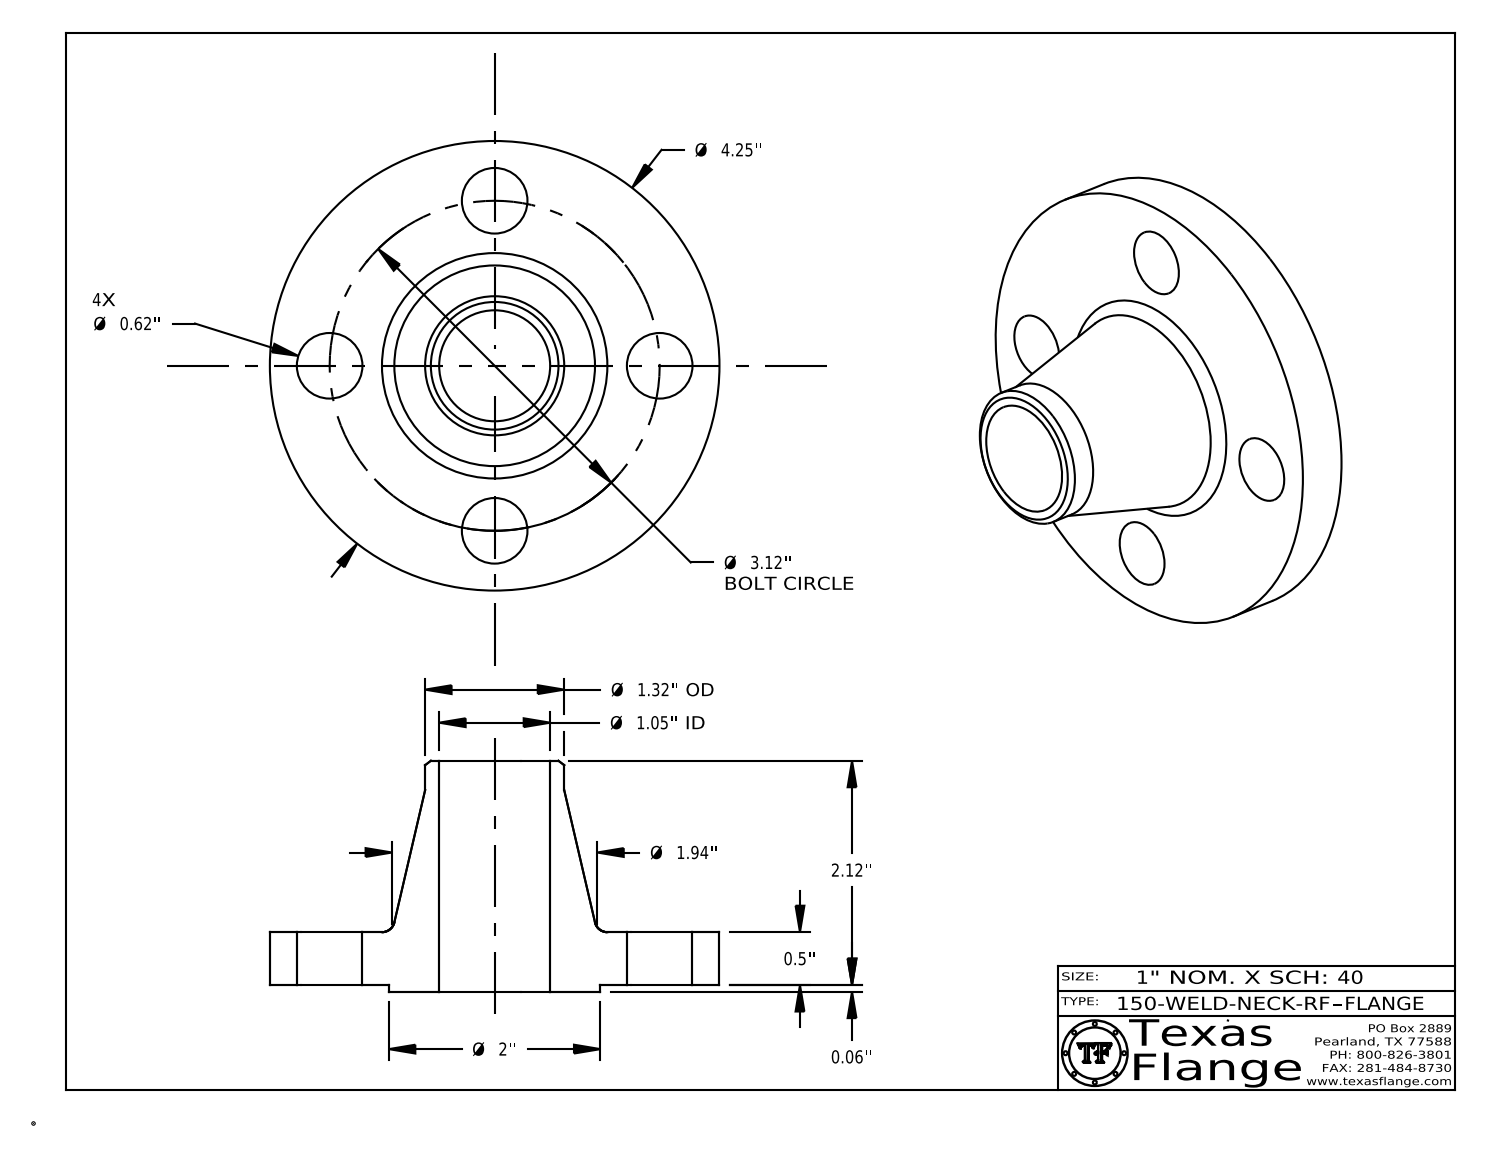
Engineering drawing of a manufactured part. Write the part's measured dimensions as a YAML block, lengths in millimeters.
part_name: "150-WELD-NECK-RF"
step_written_by: "CATIA V5 STEP AP214 (AUTOMOTIVE_DESIGN)"
units: millimeters
bodies: {solids: 1, faces: 411, planar: 369, cylindrical: 36, other: 6}
overall_size: [108, 108, 55.4]
volume: 131200
surface_area: 31470
round_holes:
  - {diameter: 15.7, count: 4}
  - {diameter: 12.6, count: 1}
  - {diameter: 26.6, count: 1}
round_bosses_or_shafts:
  - {diameter: 0.8, count: 8}
  - {diameter: 108, count: 1}
  - {diameter: 50.8, count: 1}
  - {diameter: 33.4, count: 1}
  - {diameter: 9.9, count: 1}
face_to_face_distances: [12.7, 1.6, 14.3, 55.4, 53.8, 41.1, 13.9, 12.3, 0.4, 41.5]
hole_center_spacings: [39.6, 56, 30.3, 73.2, 79.2, 39.6]
